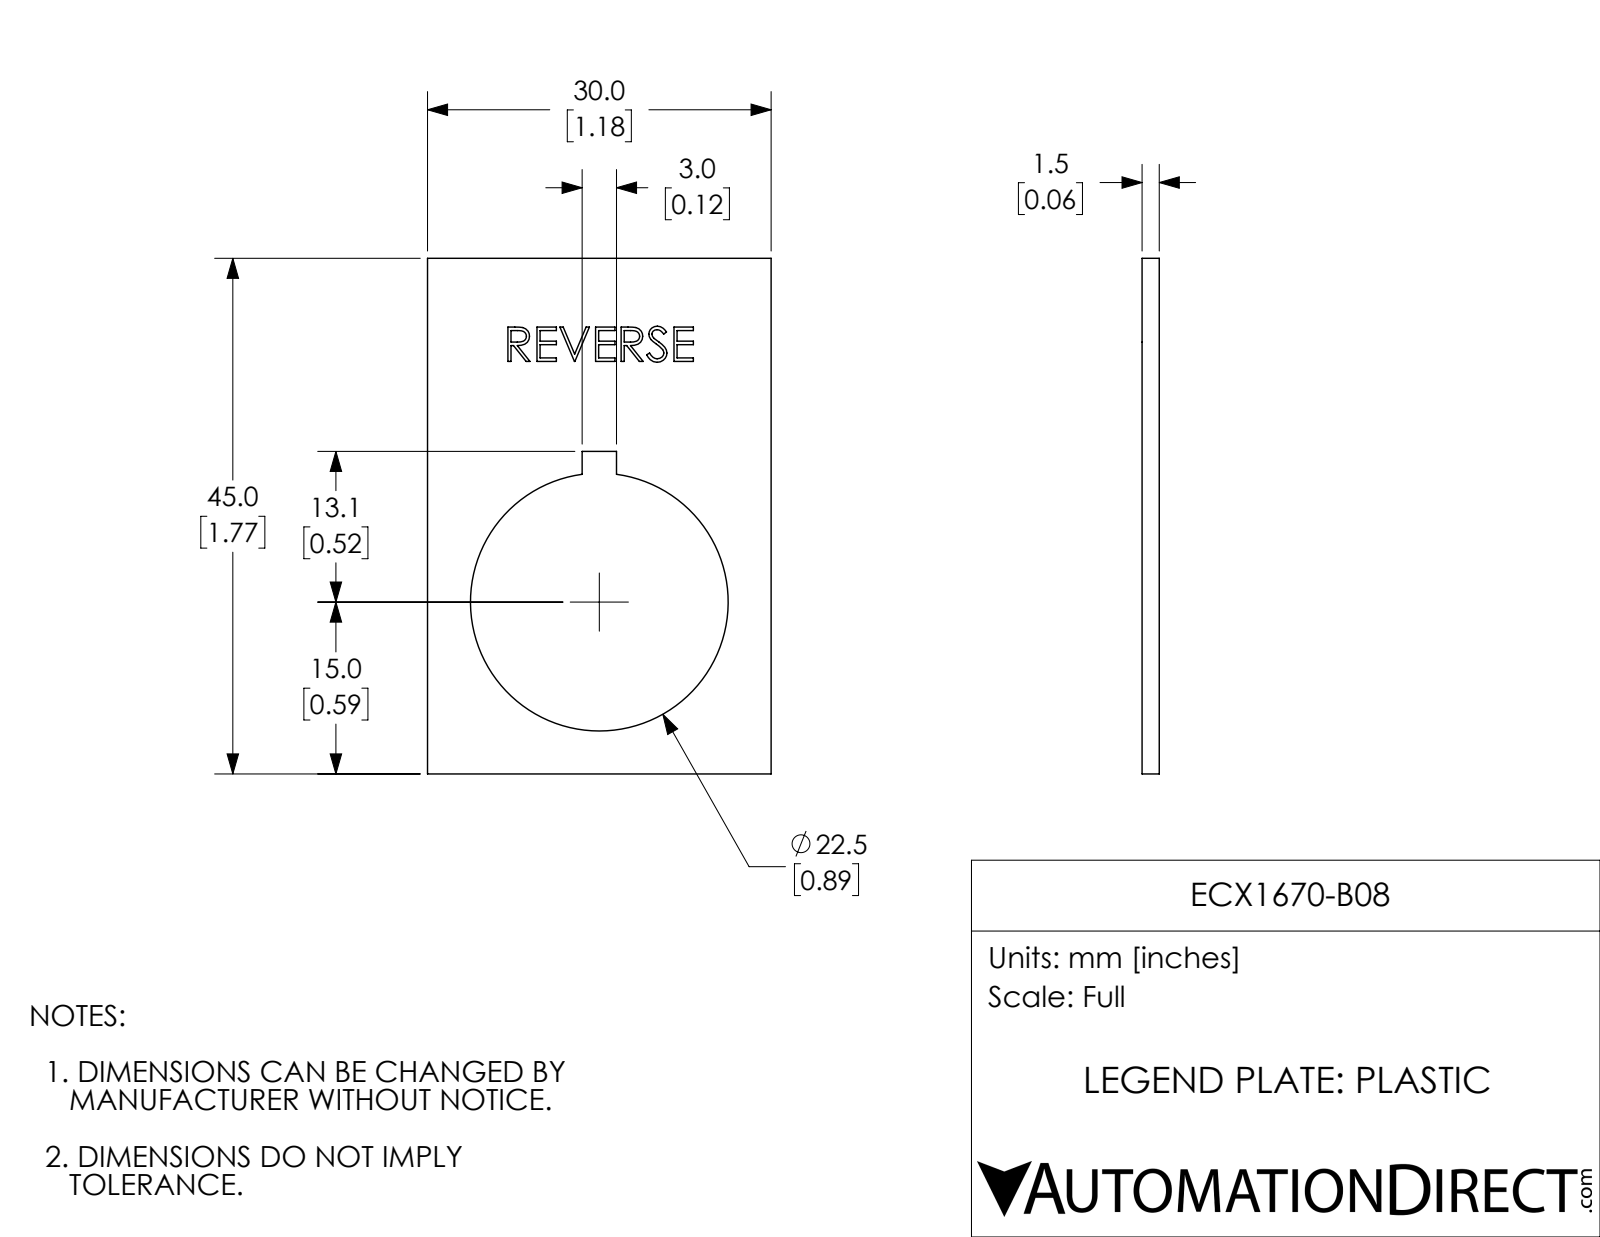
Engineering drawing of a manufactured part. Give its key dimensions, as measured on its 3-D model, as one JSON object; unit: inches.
{"part_name": "ECX1670-B08", "step_written_by": "SolidWorks 2017 (AUTOMOTIVE_DESIGN)", "units": "inches", "bodies": {"solids": 1, "faces": 113, "planar": 85, "cylindrical": 3, "other": 25}, "overall_size": [1.772, 1.181, 0.059], "volume_in3": 0.087, "surface_area_in2": 3.461, "round_holes": [[0.886, 1]], "face_to_face_distances": [0.059, 1.181, 1.772, 0.058, 0.531, 0.65, 1.108, 0.663, 0.118, 0.012]}
